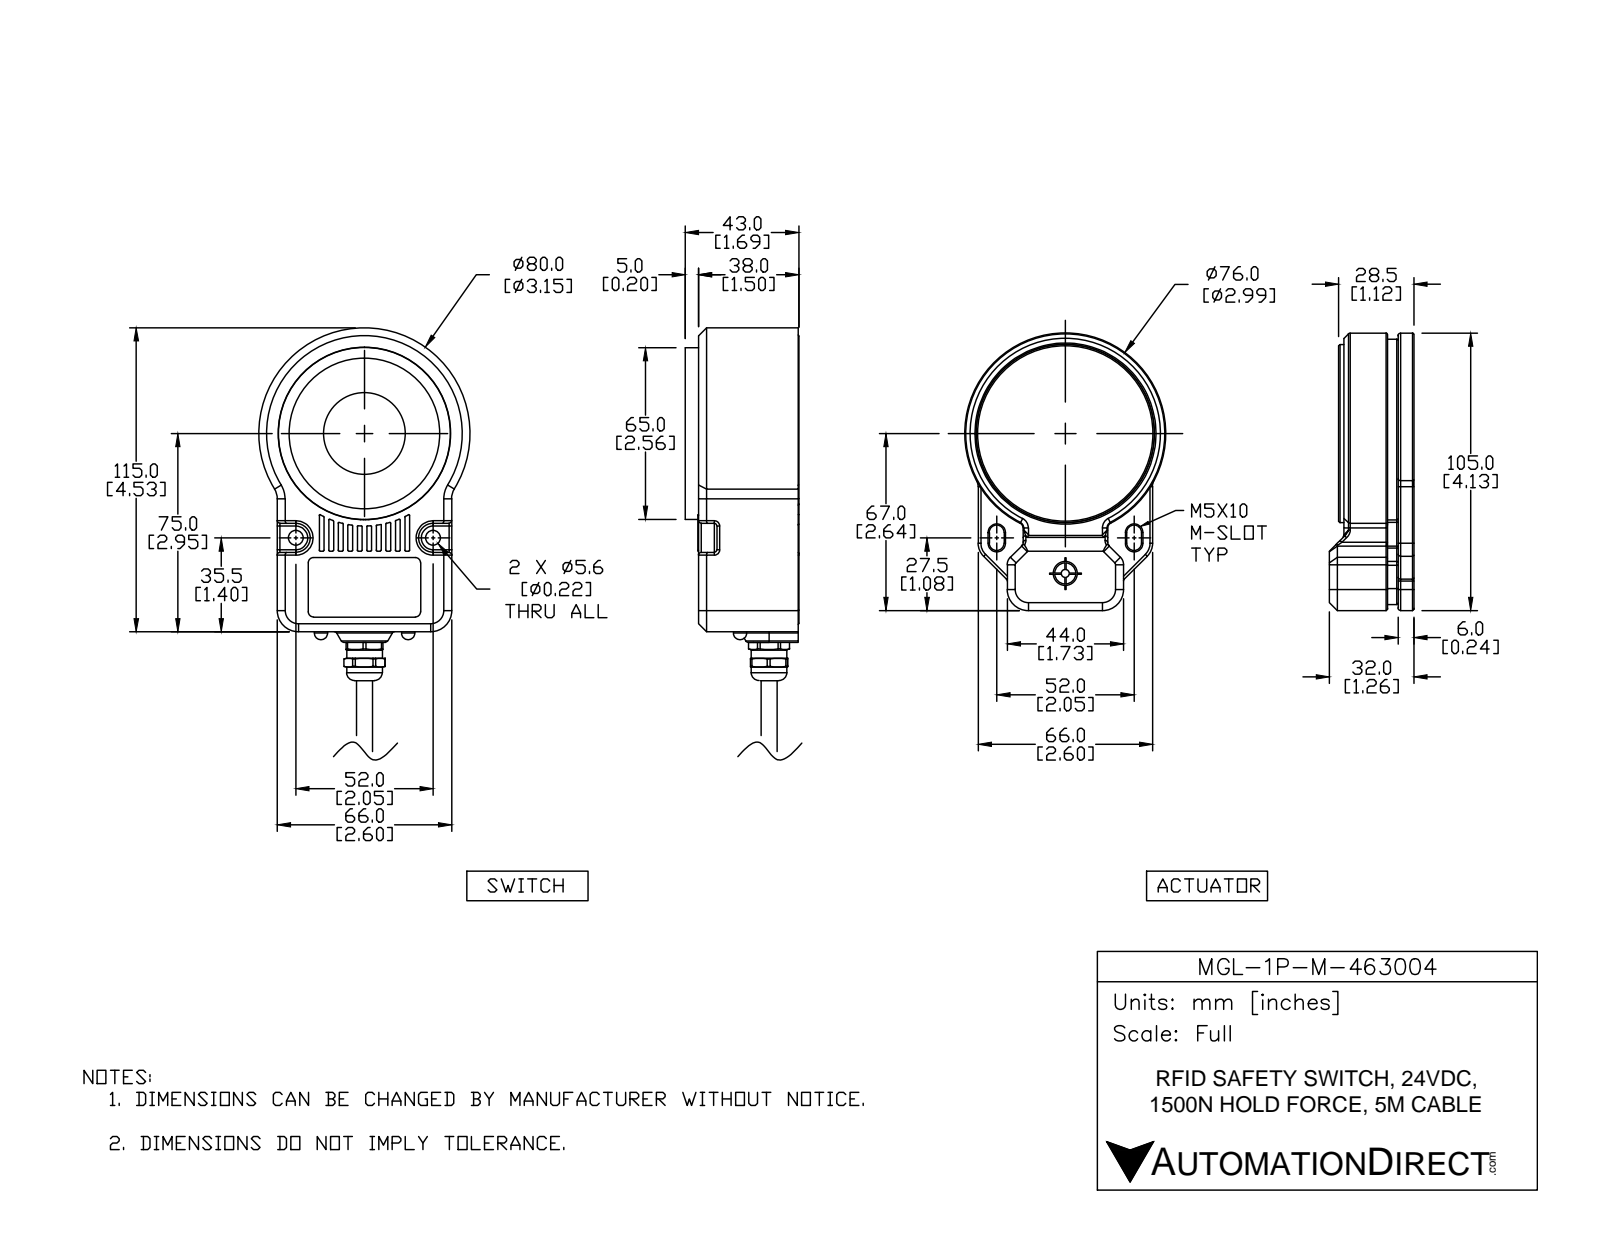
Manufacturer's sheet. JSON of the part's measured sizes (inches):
{"part_name": "MGL-1P-M-463004; MGL-1P-M-463004_2; MGL-1P-M-463004_1", "step_written_by": "SolidWorks 2017 (AUTOMOTIVE_DESIGN)", "units": "inches", "bodies": {"solids": 17, "faces": 1674, "planar": 449, "cylindrical": 708, "other": 517}, "overall_size": [8.163, 3.15, 2.854], "volume_in3": 18.96, "surface_area_in2": 210.2, "round_holes": [[0.197, 6], [0.453, 5], [0.094, 4], [0.315, 3], [0.079, 2], [0.13, 2], [0.22, 2], [0.276, 2], [0.354, 2], [0.157, 1], [0.252, 1], [0.266, 1]], "round_bosses_or_shafts": [[0.02, 4], [0.472, 3], [0.079, 3], [0.228, 2], [0.213, 2], [0.154, 2], [0.047, 2], [2.992, 1]], "partial_cylinders_radius": [[0.02, 187], [0.039, 75], [0.012, 39], [0.079, 18], [0.024, 7], [0.315, 7], [0.157, 6], [0.217, 6]], "face_to_face_distances": [0.236, 0.315, 0.098, 2.303, 2.618, 0.413, 2.205, 0.118, 0.65, 2.854], "hole_center_spacings": [0.787, 0.984, 1.392, 1.364, 0.173, 0.349, 0.4, 0.406]}
